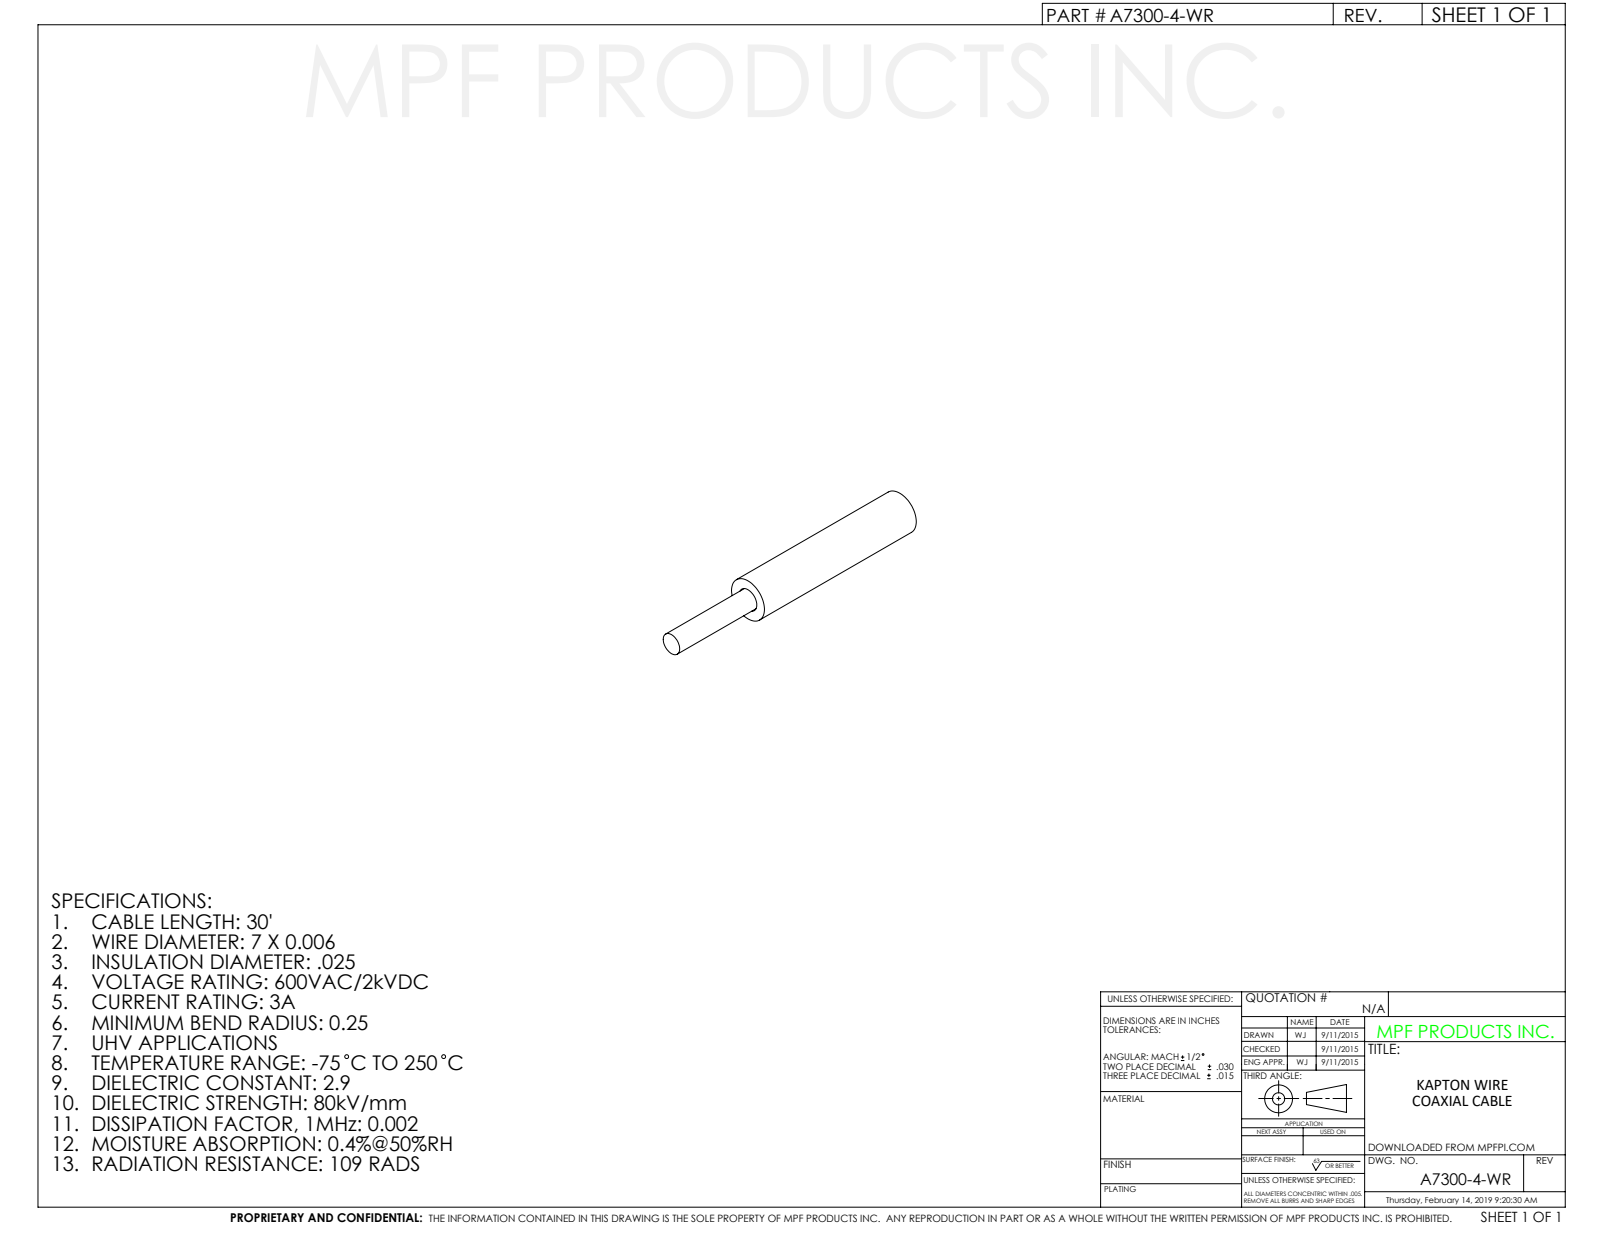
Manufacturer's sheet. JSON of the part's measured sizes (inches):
{"part_name": "A7300-4-WR", "step_written_by": "SolidWorks 2012 (CONFIG_CONTROL_DESIGN)", "units": "inches", "bodies": {"solids": 10, "faces": 42, "planar": 20, "cylindrical": 0, "other": 22}, "overall_size": [1.192, 1.051, 0.24], "volume_in3": 0.029, "surface_area_in2": 2.548, "face_to_face_distances": [0.6]}
